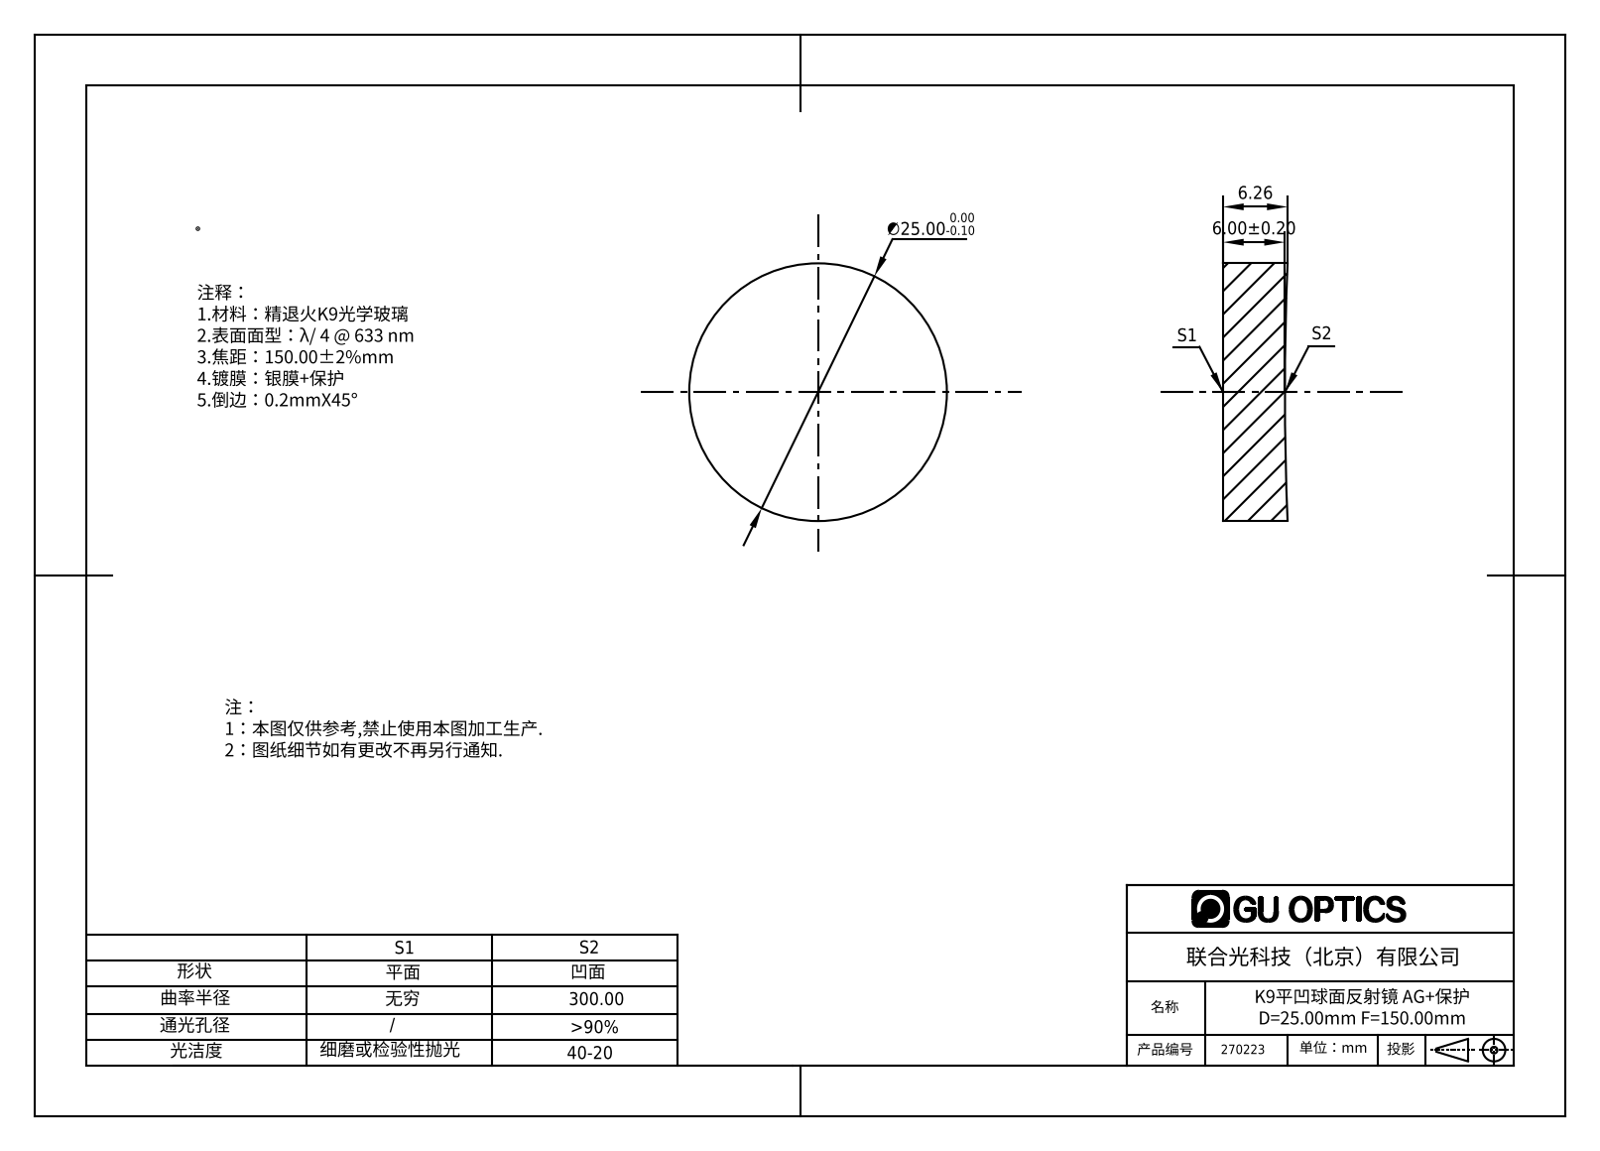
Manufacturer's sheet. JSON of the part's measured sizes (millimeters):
{"part_name": "270028", "step_written_by": "SolidWorks 2016 (AUTOMOTIVE_DESIGN)", "units": "millimeters", "bodies": {"solids": 1, "faces": 5, "planar": 1, "cylindrical": 2, "other": 2}, "overall_size": [25, 25, 6.26], "volume_mm3": 3009, "surface_area_mm2": 1474, "round_bosses_or_shafts": [[25, 1]]}
